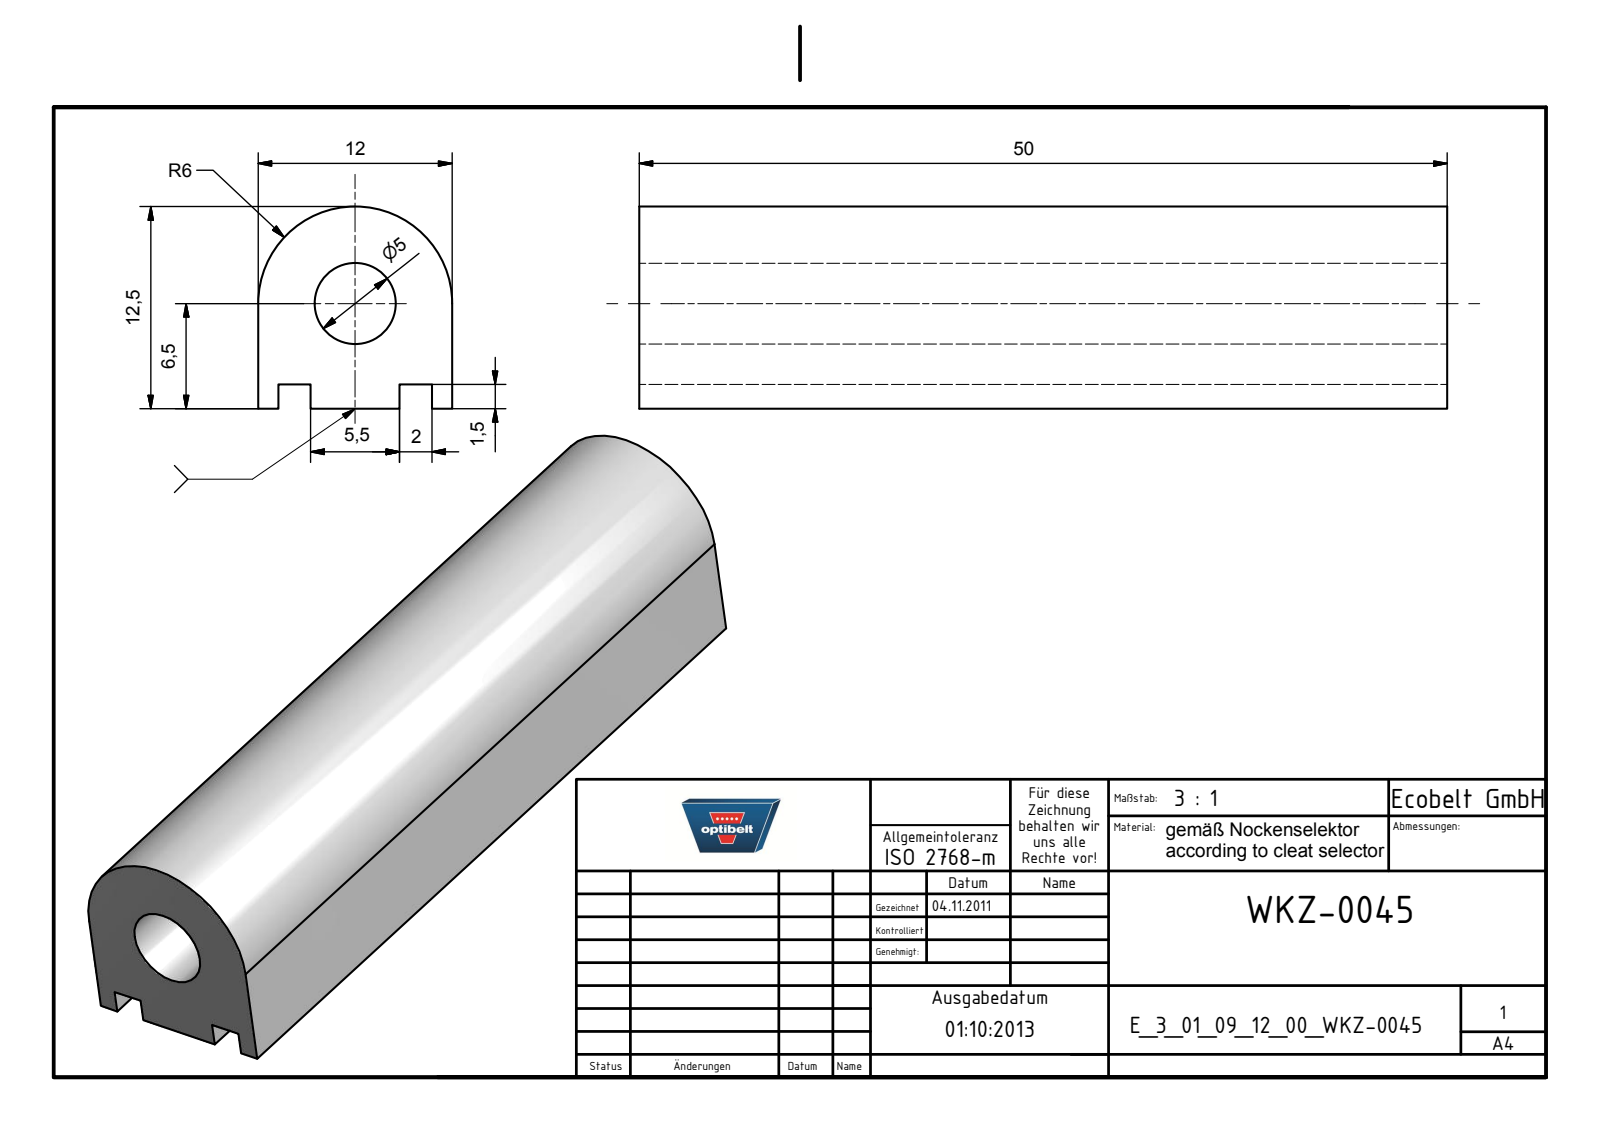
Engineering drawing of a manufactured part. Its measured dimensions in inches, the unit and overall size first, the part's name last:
Units: inches
Overall size (bounding box): 1.969 × 0.492 × 0.472
Round holes (diameter × count): ⌀0.197 ×1
Partial cylindrical surfaces — rounded edges, fillets, slot ends (radius × count): R0.236 ×1
Main face-to-face distances: 0.472, 0.059, 0.049, 0.128, 0.344, 0.423, 0.079, 0.295, 1.969, 0.374
Volume: 0.332 in³ · Surface area: 5.419 in²
Bodies: 1 solid, 15 faces (13 planar, 2 cylindrical, 0 other)
Part name (STEP PRODUCT): E_3_01_09_12_00_WKZ-0045
STEP written by: Autodesk Inventor 2025 (AUTOMOTIVE_DESIGN)
